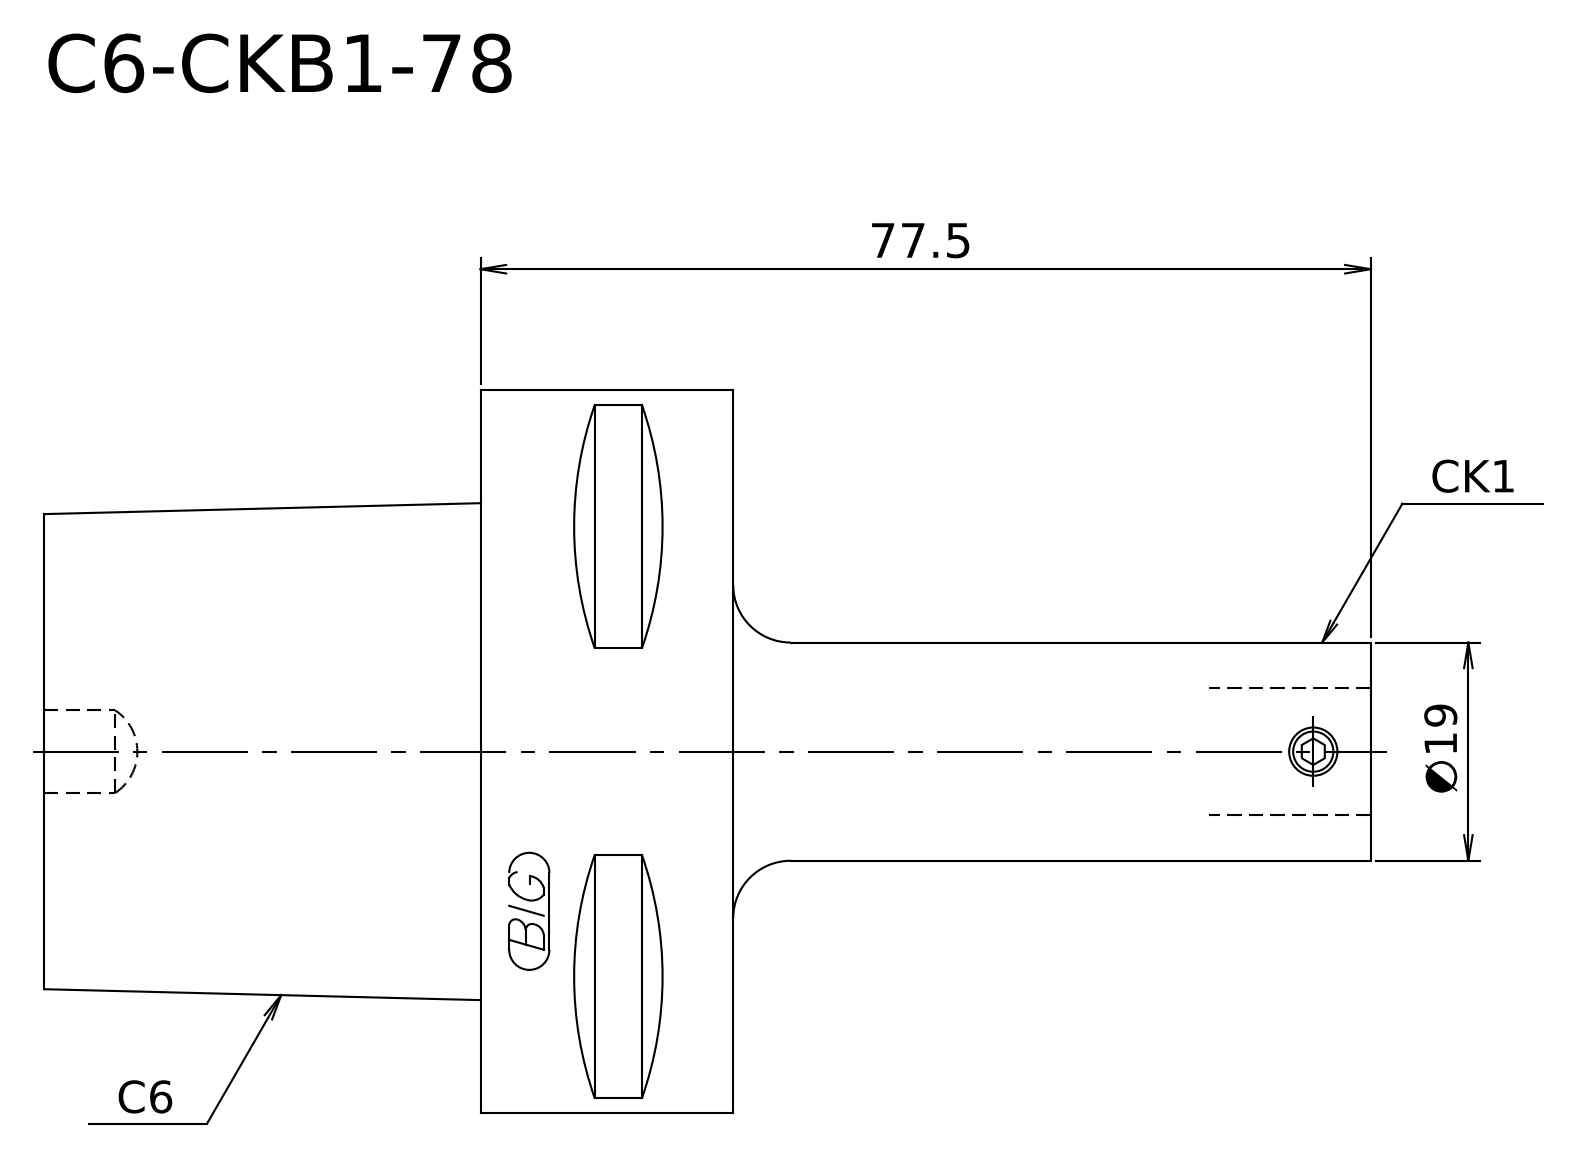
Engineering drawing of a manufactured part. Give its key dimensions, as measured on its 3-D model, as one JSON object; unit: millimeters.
{"step_written_by": "Kubotek KeyCreator V8.5.1 (14335) (CONFIG_CONTROL_DESIGN)", "units": "millimeters", "bodies": {"solids": 1, "faces": 10, "planar": 4, "cylindrical": 2, "other": 4}, "overall_size": [115.5, 62.98, 62.98], "volume_mm3": 139927, "surface_area_mm2": 18784, "round_bosses_or_shafts": [[62.98, 1], [19, 1]], "face_to_face_distances": [22, 60, 38, 55.5, 77.5, 115.5]}
